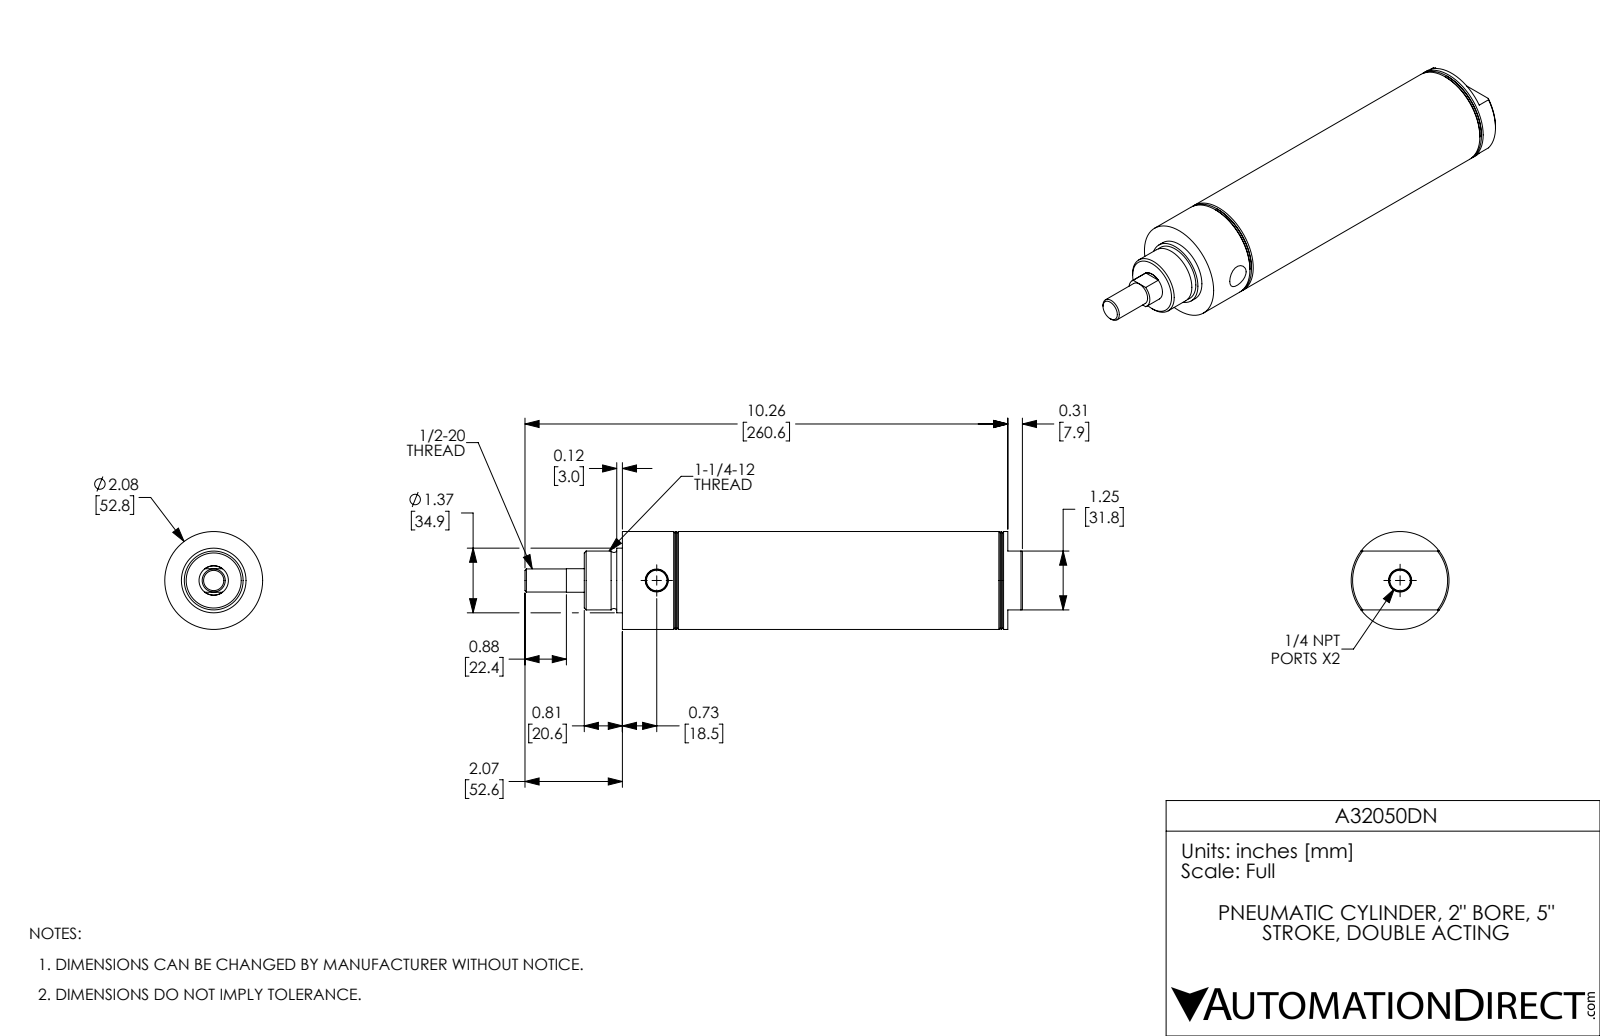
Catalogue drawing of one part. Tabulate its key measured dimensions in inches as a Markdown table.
| quantity | value |
| --- | --- |
| part name | A32050DN-MainBody; A32050DN-Rod; A32050DN |
| STEP written by | SolidWorks 2017 (AUTOMOTIVE_DESIGN) |
| units | inches |
| bodies | 2 solids, 77 faces (20 planar, 24 cylindrical, 33 other) |
| overall size | 10.57 × 2.08 × 2.08 |
| volume | 15.43 in³ |
| surface area | 138.2 in² |
| round holes (diameter × count) | 0.438 × 2, 0.625 × 1, 2 × 1 |
| round bosses / shafts (diameter × count) | 2.08 × 1, 1.373 × 1, 1.25 × 1, 0.491 × 1 |
| main face-to-face distances | 1.5, 7, 0.5, 5.5, 5, 2, 8.5, 6.5, 0.31, 1.19 |
